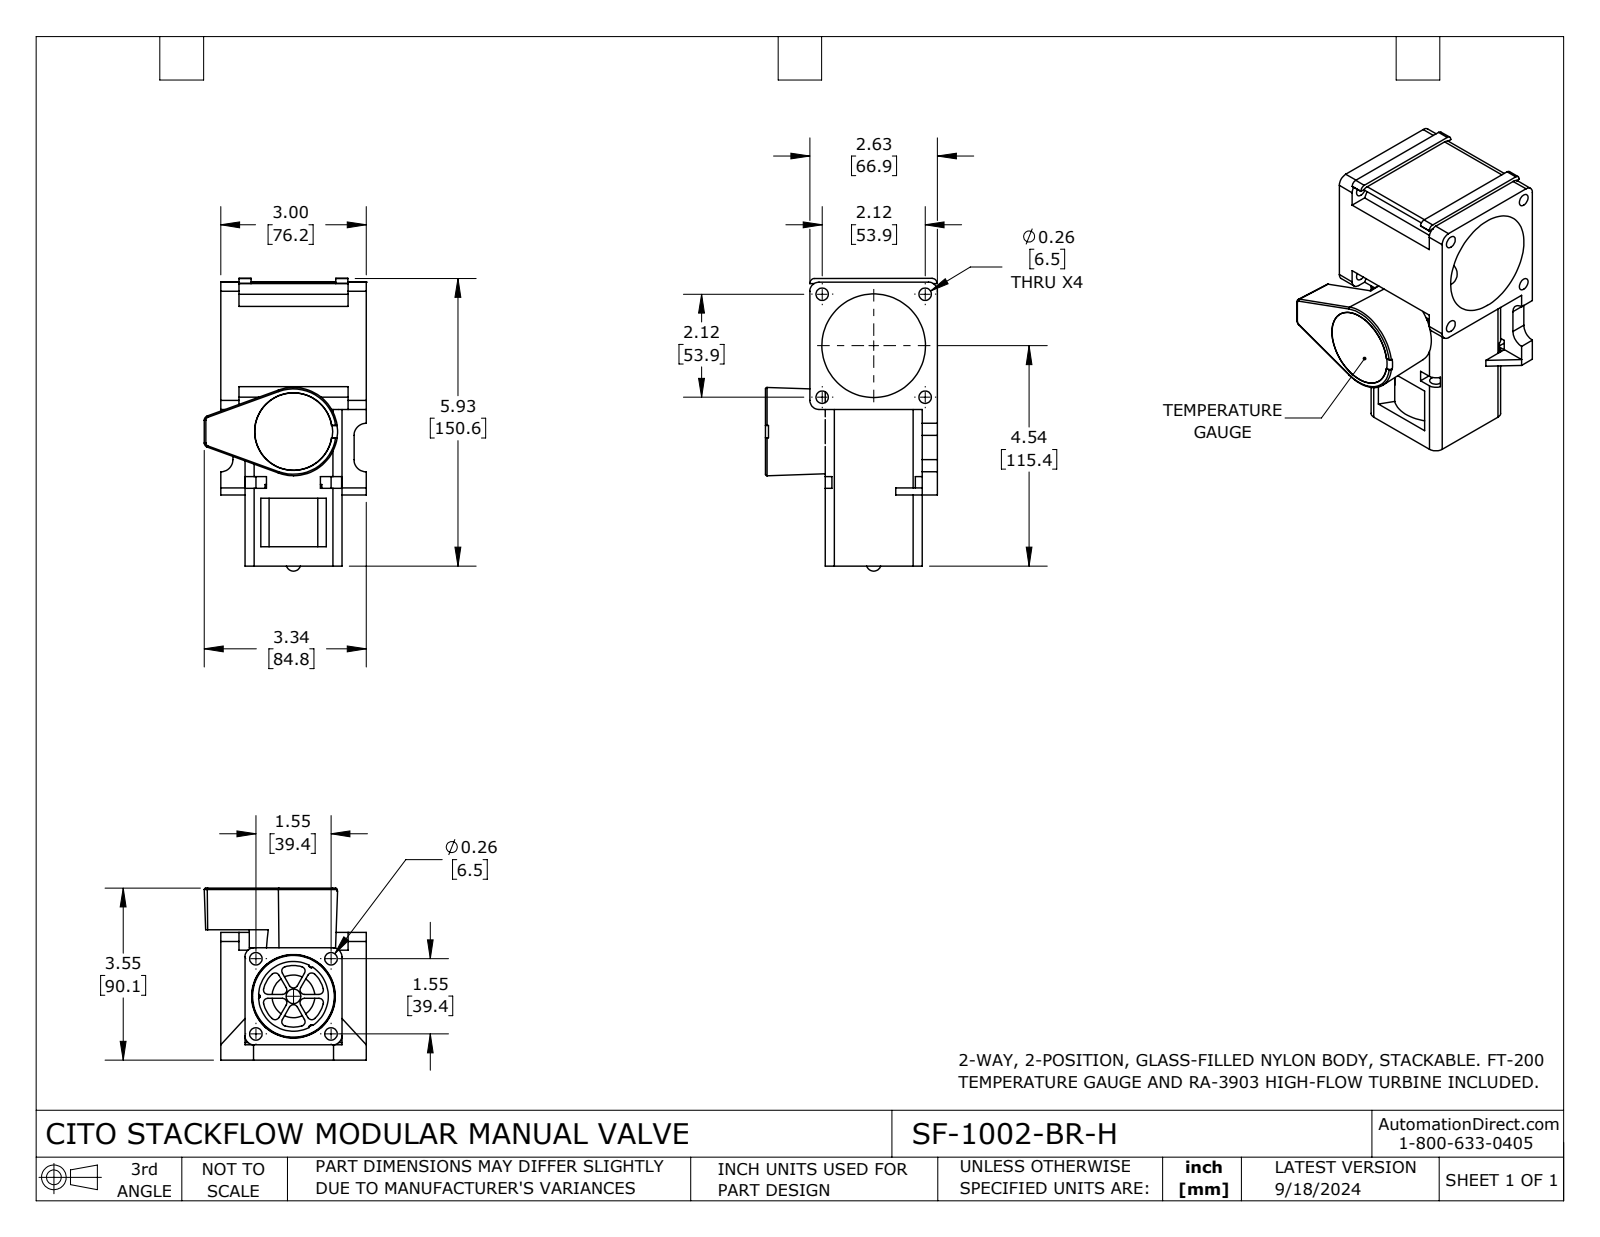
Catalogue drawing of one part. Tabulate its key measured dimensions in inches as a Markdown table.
| quantity | value |
| --- | --- |
| part name | SF-1002-BR-H |
| STEP written by | SolidWorks 2023 (CONFIG_CONTROL_DESIGN) |
| units | inches |
| bodies | 5 solids, 410 faces (173 planar, 205 cylindrical, 32 other) |
| overall size | 6.031 × 3.547 × 3.338 |
| volume | 19.15 in³ |
| surface area | 174 in² |
| round holes (diameter × count) | 0.256 × 4, 0.257 × 4, 0.124 × 1, 0.52 × 1, 0.88 × 1, 1.284 × 1, 1.477 × 1, 1.484 × 1, 1.595 × 1, 1.723 × 1, 2.136 × 1 |
| round bosses / shafts (diameter × count) | 1.6 × 1, 1.45 × 1, 0.125 × 1 |
| partial cylindrical surfaces (radius × count) | 0.092 × 18, 0.046 × 6, 0.25 × 4, 0.03 × 3, 0.187 × 3, 0.01 × 2, 0.02 × 2, 0.1 × 2 |
| main face-to-face distances | 2, 0.316, 2.316, 2.5, 0.5, 2.632, 0.915, 3.231, 3.547, 3 |
| hole center spacings | 1.502, 2.124, 1.096, 1.096, 1.55, 1.55, 2.192, 3.003 |
